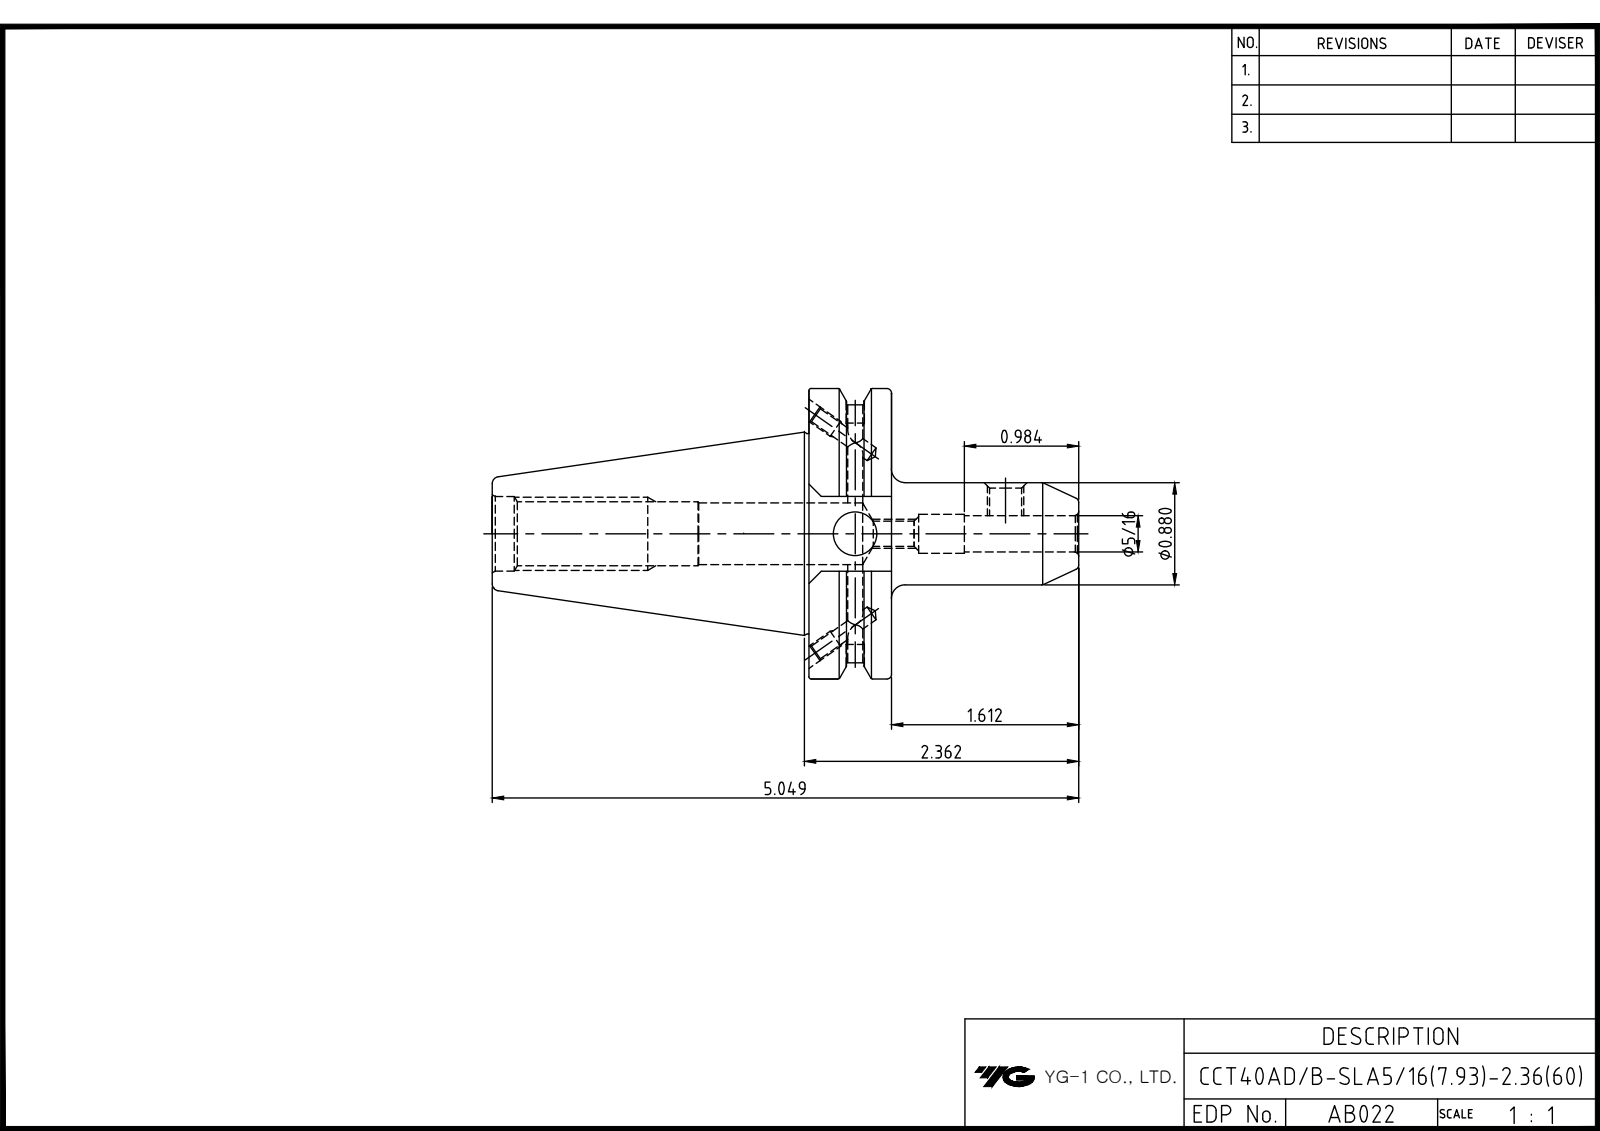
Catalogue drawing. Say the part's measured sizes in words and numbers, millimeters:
The part is named "LO-CCT40ADB-SLA7.9375-60". Its 3-D file was written by "Autodesk Inventor 2025 (AUTOMOTIVE_DESIGN)". It is 1 solid with 92 faces: 39 planar, 29 cylindrical and 24 other. Overall it measures 128.25 by 63.5 by 61.09 millimeters. Its volume is 117 004 cubic millimeters and its surface area 24 672 square millimeters. Round holes: 4 of diameter 3.24, 2 of diameter 4, 2 of diameter 4.2, 1 of diameter 5.36, 1 of diameter 6.78, 1 of diameter 7.94, 1 of diameter 9.14, 1 of diameter 9.53, 1 of diameter 13.39, 1 of diameter 16.3. Round bosses or shafts: 1 of diameter 63.5, 1 of diameter 43.8, 1 of diameter 22.35. Partial cylindrical surfaces (rounded edges, fillets, slot ends): 1 of radius 28.15. The main face-to-face distances are 18.05, 47.6, 16.38, 69.25, 87.3, 81.29, 12.04, 6.01, 77.46, 8.21.
